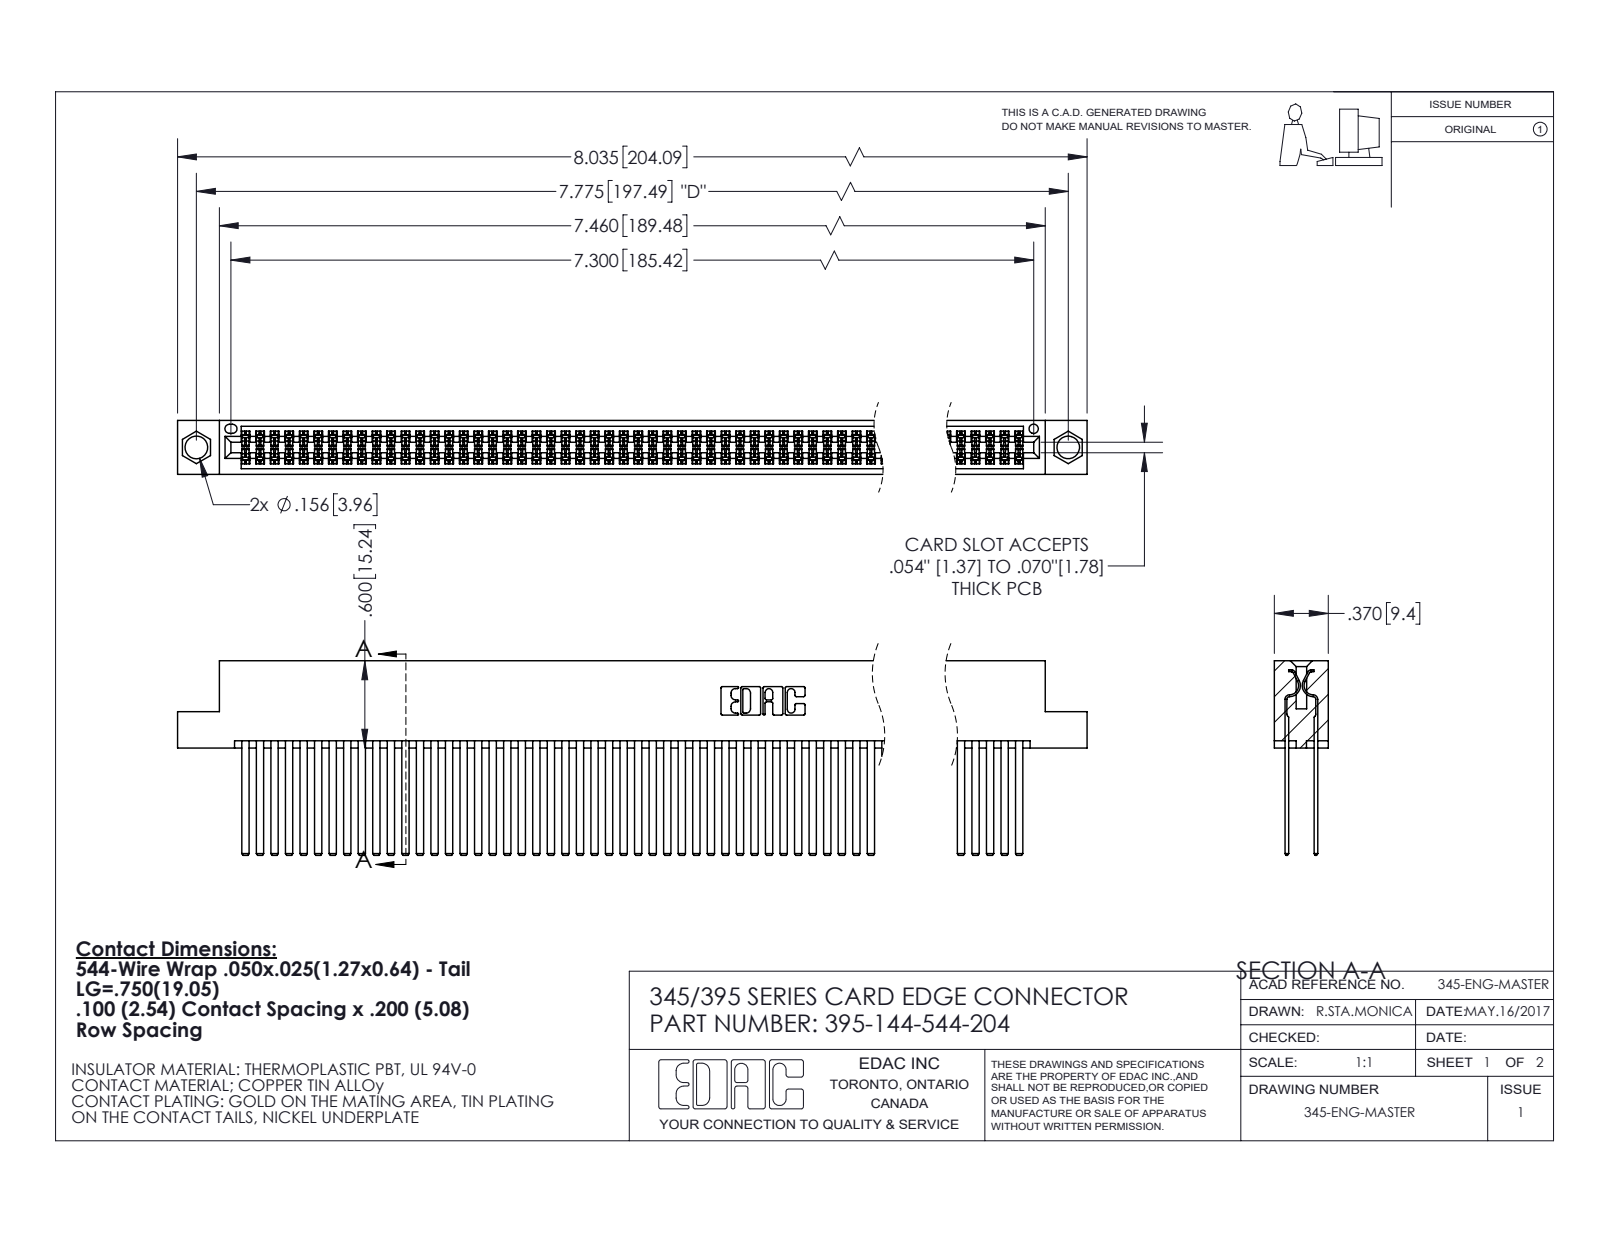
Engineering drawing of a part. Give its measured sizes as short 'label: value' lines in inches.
name: 345 Part_Flush Mounting Lugs - 0.156 Dia-TI; 395-144-544-204; 345-292-001_345-293-144
written by: SolidWorks 2020 (CONFIG_CONTROL_DESIGN)
unit: in
bodies: 145 solids, 6476 faces (4270 planar, 2206 cylindrical, 0 other)
size: 8.035 × 1.337 × 0.37
volume: 1.344 in³; area: 60.28 in²
holes: 2× ⌀0.156, 1× ⌀0.064
rounds: 216× R0.006, 22× R0.01, 6× R0.007, 6× R0.031, 3× R0.026, 2× R0.014, 2× R0.019, 2× R0.022
face distances: 0.2, 0.025, 0.072, 0.098, 0.272, 0.298, 0.225, 0.175, 0.37, 0.05
hole spacings: 0.27, 7.539, 7.775
